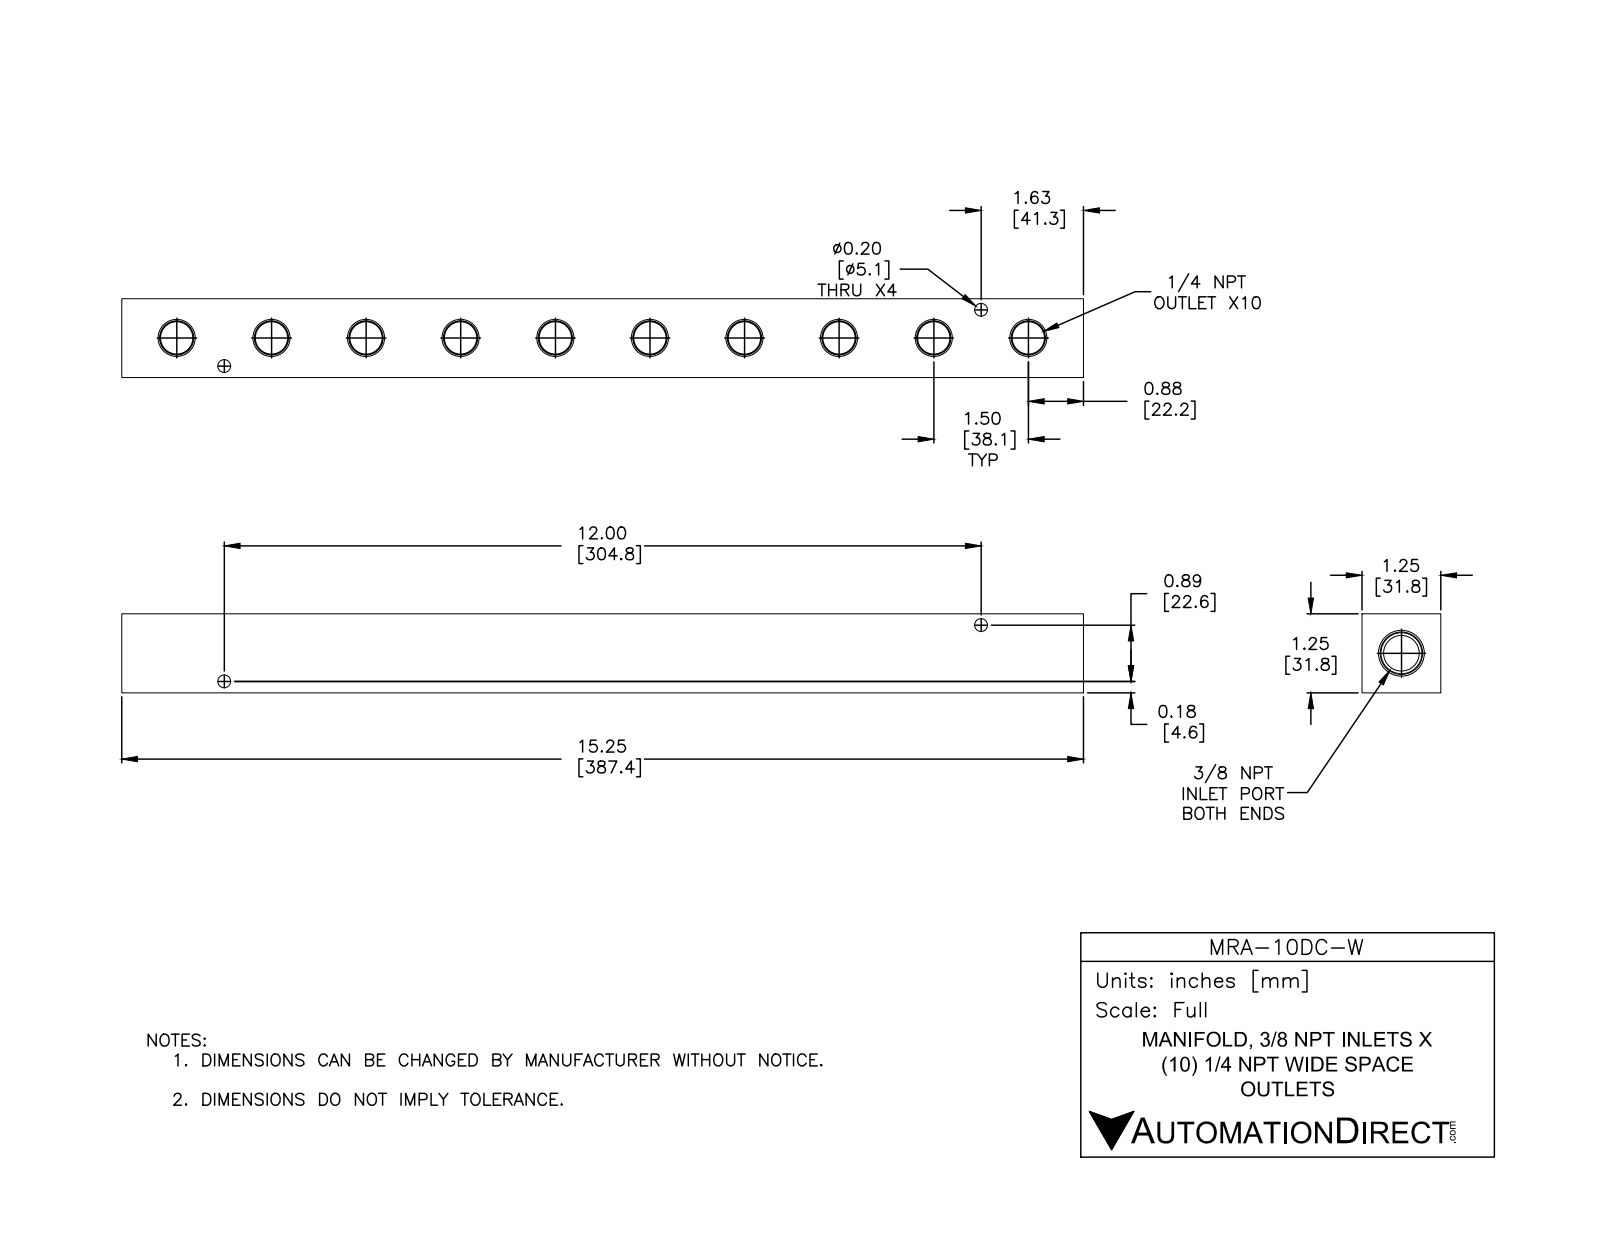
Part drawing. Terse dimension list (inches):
name: MRA-10DC-W
written by: SolidWorks 2015 (CONFIG_CONTROL_DESIGN)
unit: in
bodies: 1 solid, 114 faces (28 planar, 38 cylindrical, 48 other)
size: 15.25 × 1.25 × 1.25
volume: 18.99 in³; area: 110.9 in²
holes: 4× ⌀0.2, 1× ⌀0.562
rounds: 10× R0.219
face distances: 1.25, 15.25, 0.86, 0.39, 0.41, 14.84, 14.43
hole spacings: 12.033
